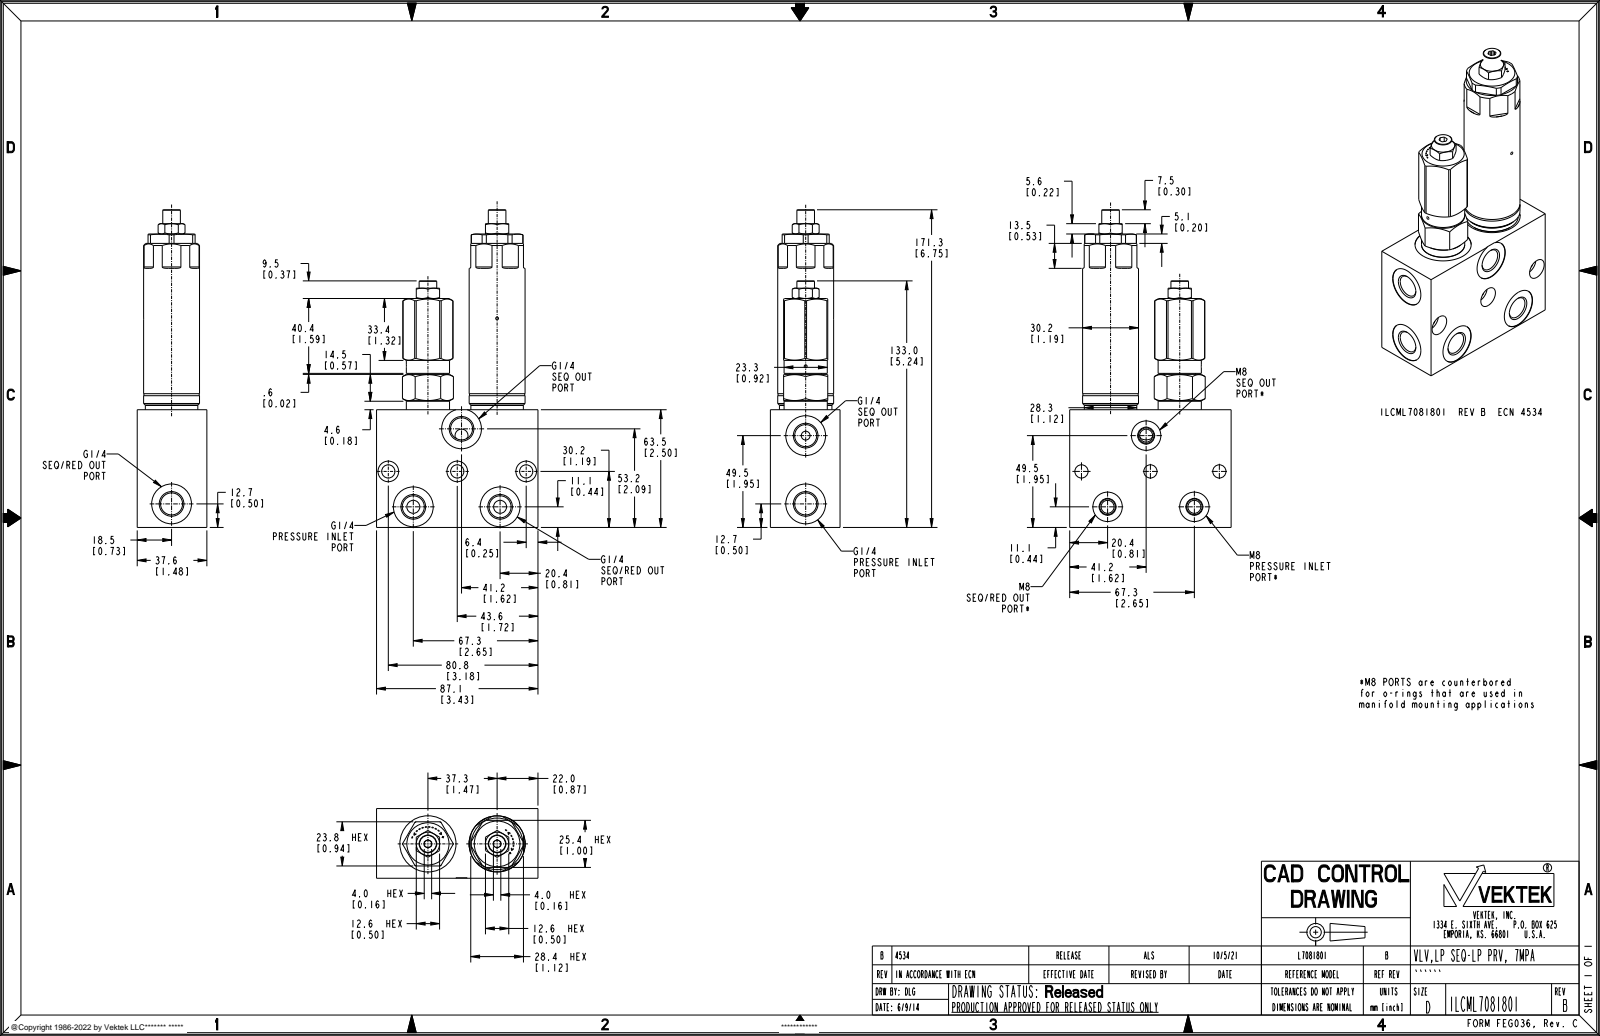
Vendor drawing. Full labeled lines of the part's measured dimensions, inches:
Part name (STEP PRODUCT): ILCML7081801
STEP written by: PRO/ENGINEER BY PARAMETRIC TECHNOLOGY CORPORATION, 2013320 (CONFIG_CONTROL_DESIGN)
Units: inches
Bodies: 1 solid, 316 faces (104 planar, 131 cylindrical, 81 other)
Overall size (bounding box): 6.916 × 3.43 × 1.48
Volume: 17.07 in³ · Surface area: 81.3 in²
Round holes (diameter × count): ⌀0.468 ×5, ⌀0.846 ×5, ⌀0.276 ×3, ⌀0.281 ×3, ⌀0.438 ×3, ⌀0.625 ×3, ⌀0.094 ×2, ⌀0.392 ×2, ⌀1.193 ×2, ⌀0.062 ×1, ⌀0.187 ×1, ⌀0.203 ×1
Round bosses / shafts (diameter × count): ⌀0.375 ×2, ⌀1.188 ×1, ⌀1.115 ×1, ⌀0.918 ×1, ⌀0.8 ×1, ⌀0.685 ×1, ⌀0.67 ×1, ⌀0.622 ×1
Partial cylindrical surfaces — rounded edges, fillets, slot ends (radius × count): R0.428 ×1, R0.55 ×1
Main face-to-face distances: 1.48, 2.5, 3.43, 0.938, 1.561, 0.938, 1.47, 3.42, 1.869, 2.807
Hole centre spacings: 1.465, 0.05, 0.144, 0.715, 0.72, 0.765, 0.909, 0.92
